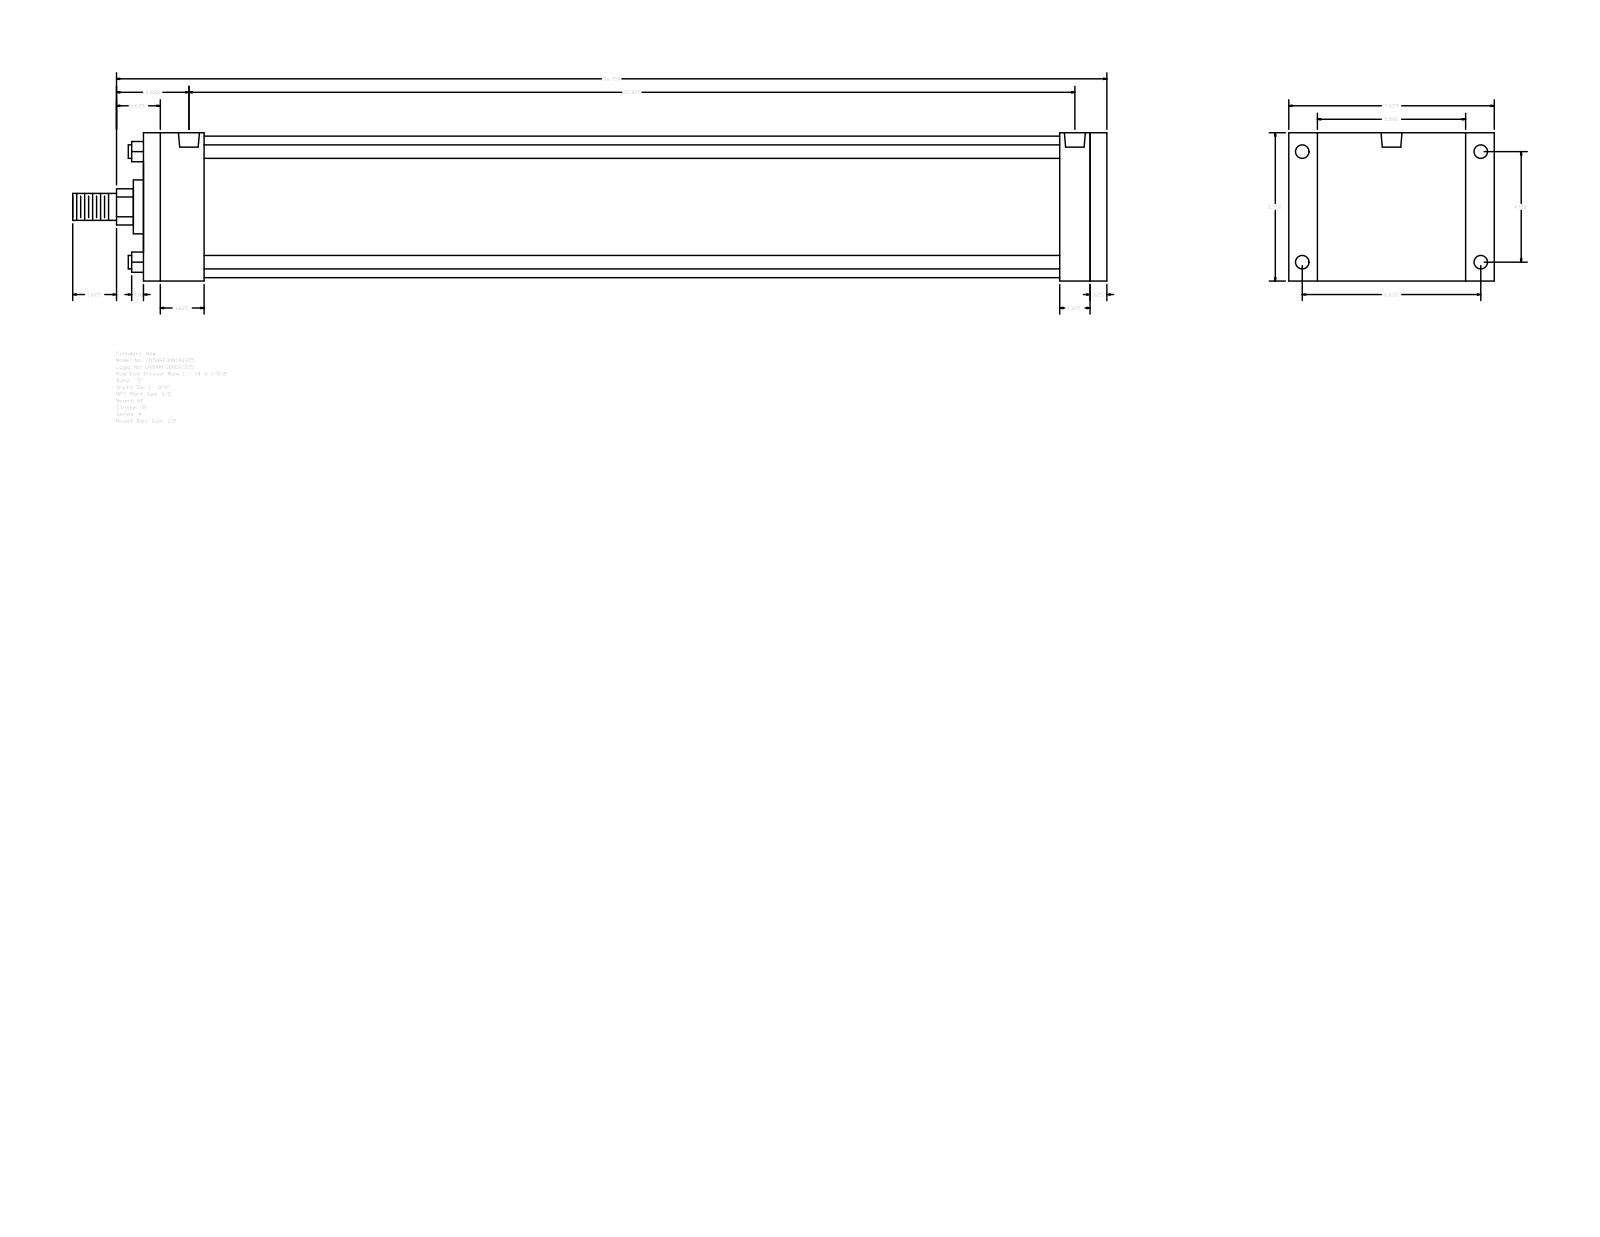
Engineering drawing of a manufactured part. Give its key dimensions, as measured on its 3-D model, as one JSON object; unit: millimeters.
{"part_name": "A_RF__0500_1.375", "step_written_by": "GSSL Pune (CONFIG_CONTROL_DESIGN)", "units": "millimeters", "bodies": {"solids": 0, "faces": 92, "planar": 64, "cylindrical": 28, "other": 0}, "overall_size": [974.73, 193.68, 139.7], "round_holes": [[8.73, 4], [12.7, 4], [19.77, 2]], "round_bosses_or_shafts": [[12.7, 4], [133.35, 1], [50.8, 1], [34.92, 1], [25.4, 1]], "partial_cylinders_radius": [[17.06, 1]], "face_to_face_distances": [139.7, 908.05, 892.18, 15.87, 57.15, 28.58, 835.03, 850.9, 863.6, 806.45], "hole_center_spacings": [2.39, 104.14, 168.28, 197.9, 830.25, 832.64, 835.03]}
